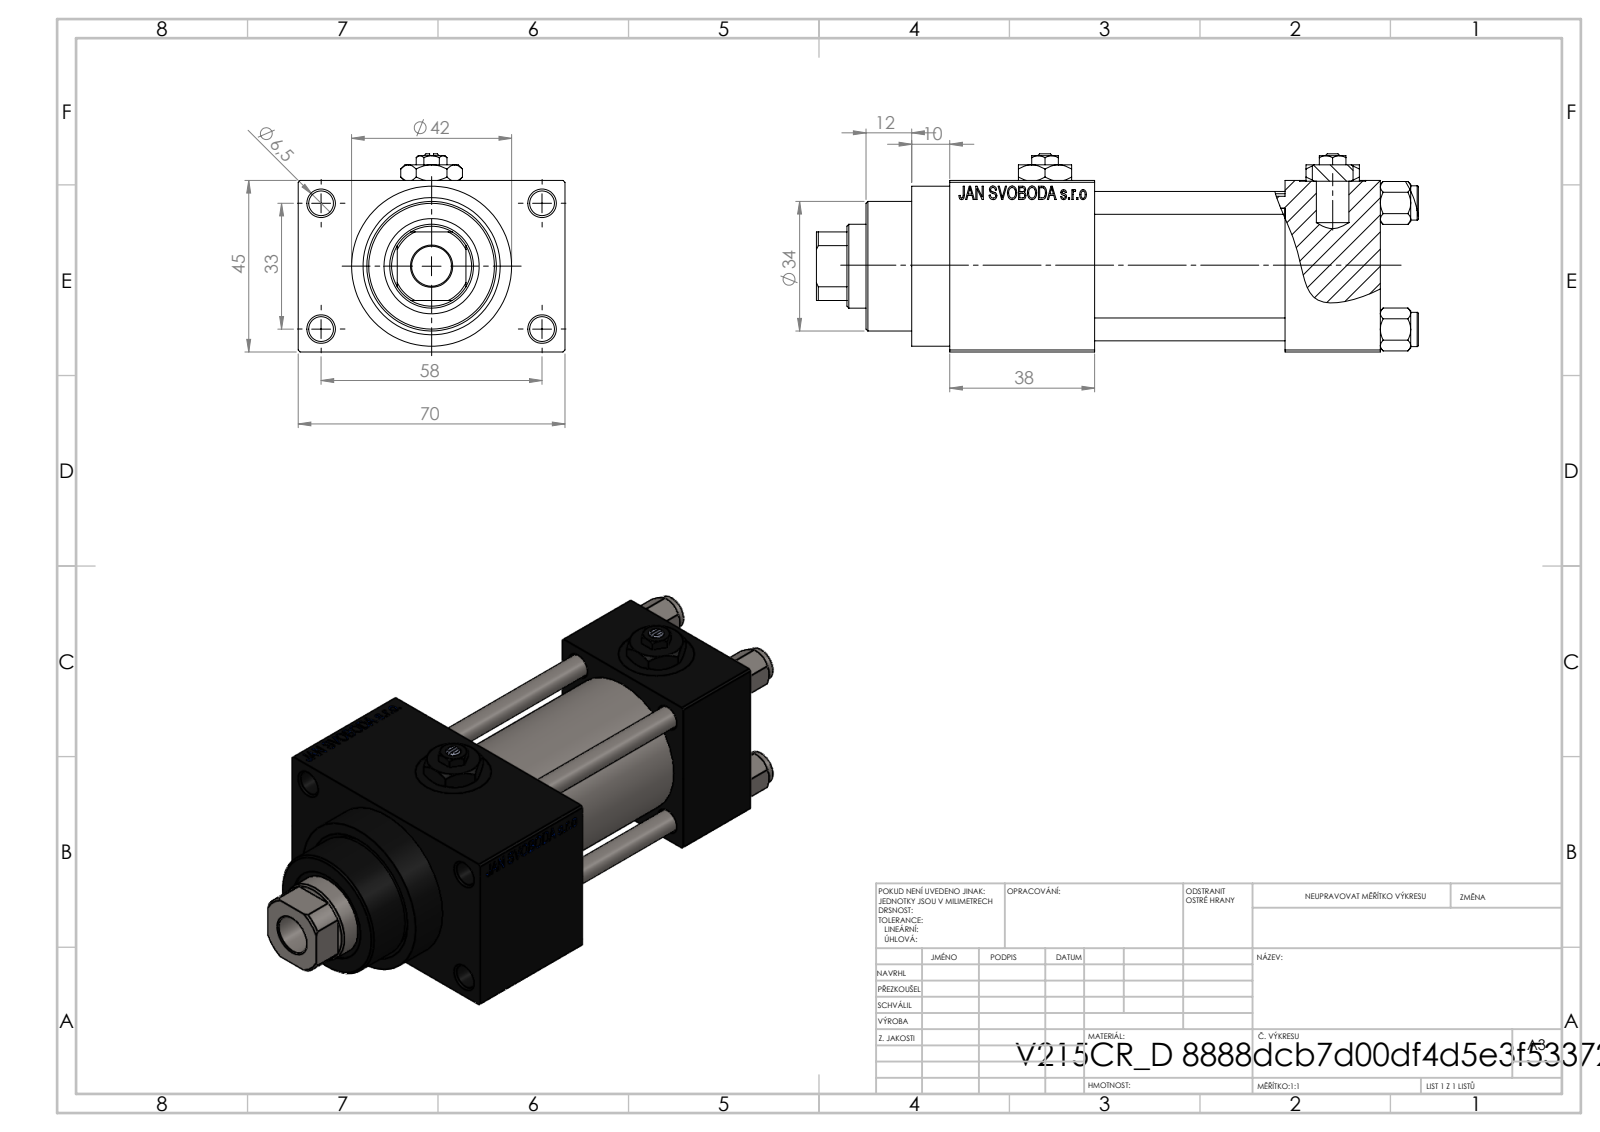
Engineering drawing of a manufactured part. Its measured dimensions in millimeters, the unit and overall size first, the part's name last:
Units: millimetres
Overall size (bounding box): 158 × 70 × 52
Round holes (diameter × count): ⌀6 ×4, ⌀6.5 ×4, ⌀13.16 ×4, ⌀20 ×4, ⌀7 ×3, ⌀10.5 ×1, ⌀22 ×1, ⌀24 ×1, ⌀25 ×1, ⌀32 ×1, ⌀33 ×1
Round bosses / shafts (diameter × count): ⌀9 ×4, ⌀42 ×1, ⌀38 ×1, ⌀34 ×1
Partial cylindrical surfaces — rounded edges, fillets, slot ends (radius × count): R10.5 ×1
Main face-to-face distances: 45, 25, 50, 12.5, 75, 57.5, 88, 38, 113, 70
Hole centre spacings: 12.4, 23.48, 33.2, 33.37, 35.35, 45.6, 56.35, 33
Volume: 98 084 mm³ · Surface area: 81 616 mm²
Bodies: 12 solids, 1203 faces (542 planar, 99 cylindrical, 562 other)
Part name (STEP PRODUCT): Zatka_pro_OIL_PORT; V215_VC_A; NUT_M5_D; V215CR_D_TYCINKA (+2 more)
STEP written by: SolidWorks 2019 (CONFIG_CONTROL_DESIGN)
